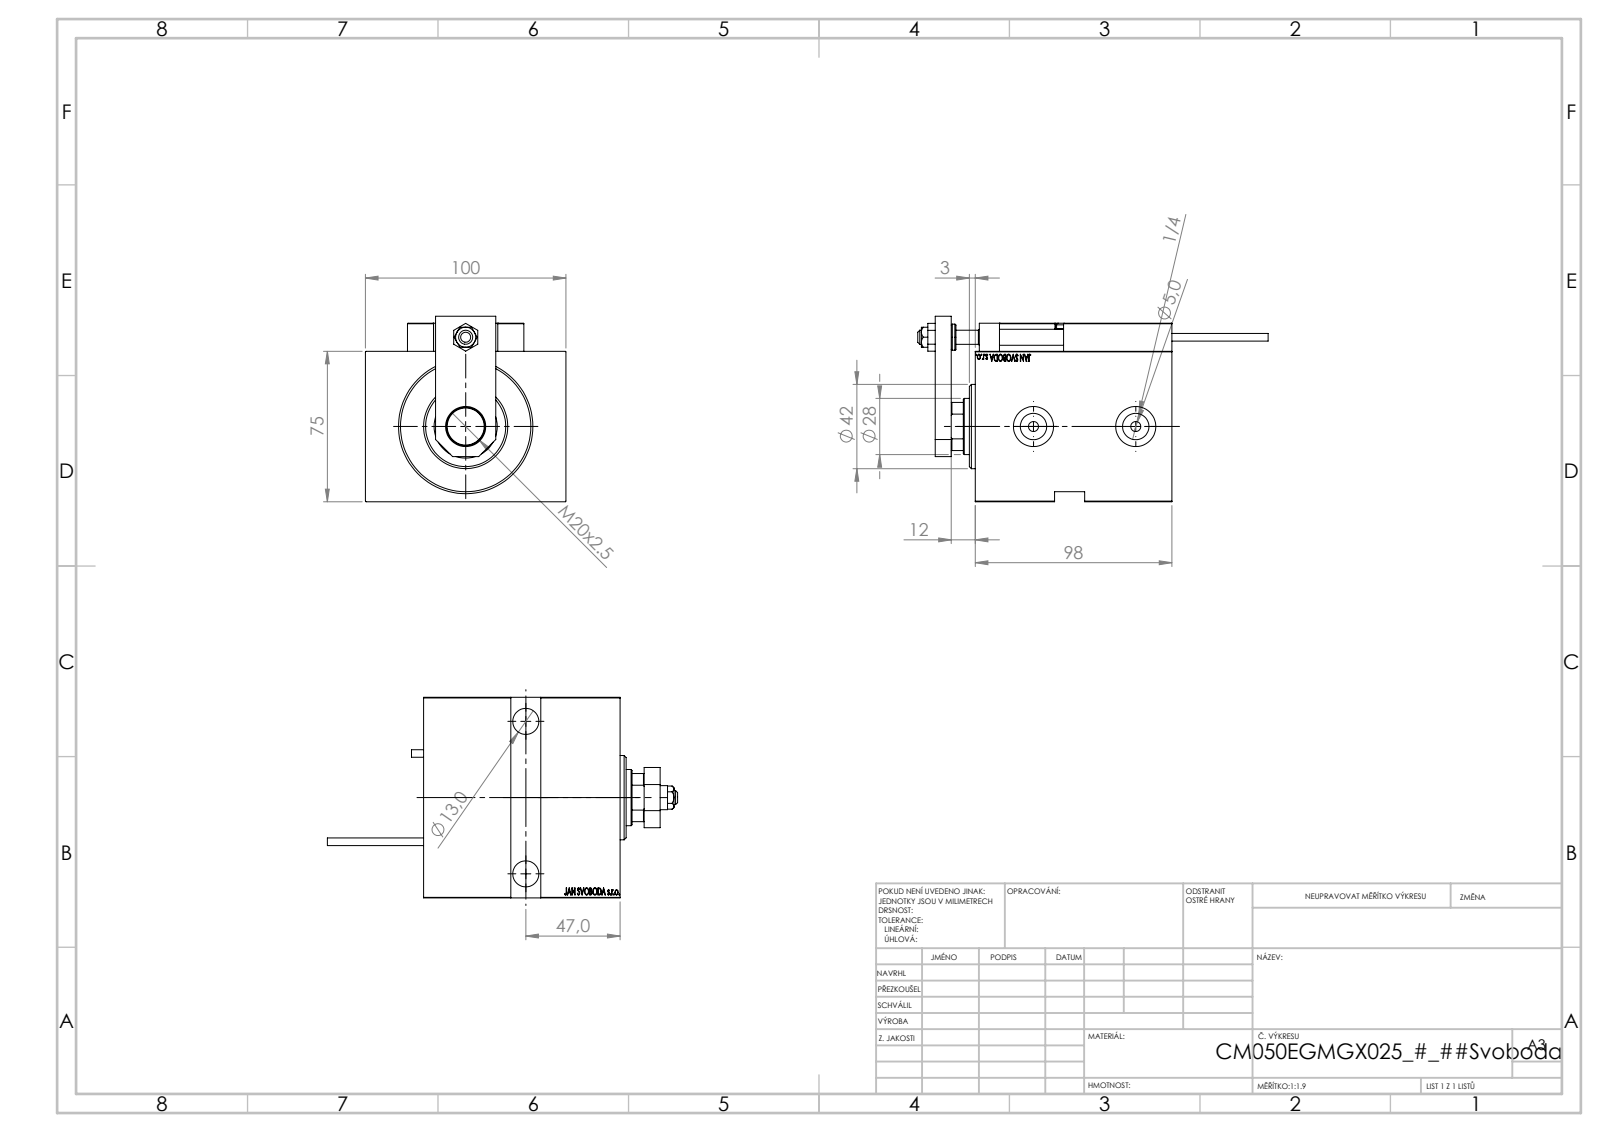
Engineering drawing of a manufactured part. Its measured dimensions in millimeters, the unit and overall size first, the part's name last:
Units: millimetres
Overall size (bounding box): 174.7 × 100 × 92.5
Round holes (diameter × count): ⌀8 ×5, ⌀3.2 ×4, ⌀4 ×4, ⌀5 ×4, ⌀20 ×3, ⌀13 ×2, ⌀13.16 ×2, ⌀19 ×2, ⌀7 ×1, ⌀18.5 ×1, ⌀28 ×1, ⌀31.5 ×1
Round bosses / shafts (diameter × count): ⌀5 ×2, ⌀3.8 ×2, ⌀52 ×1, ⌀42 ×1, ⌀13 ×1, ⌀11 ×1
Partial cylindrical surfaces — rounded edges, fillets, slot ends (radius × count): R0.3 ×30, R3 ×2, R13.5 ×1
Main face-to-face distances: 75, 14, 100, 98, 84, 5, 79, 25, 32, 12
Hole centre spacings: 11.37, 20, 29.59, 29.69, 36.06, 42.19, 48.83, 50.04
Volume: 729 848 mm³ · Surface area: 125 278 mm²
Bodies: 24 solids, 1285 faces (570 planar, 174 cylindrical, 541 other)
Part name (STEP PRODUCT): ZARAZKA; SWITCH DIM B,W; KONCOVKA; NUT_D10 (+7 more)
STEP written by: SolidWorks 2019 (CONFIG_CONTROL_DESIGN)
